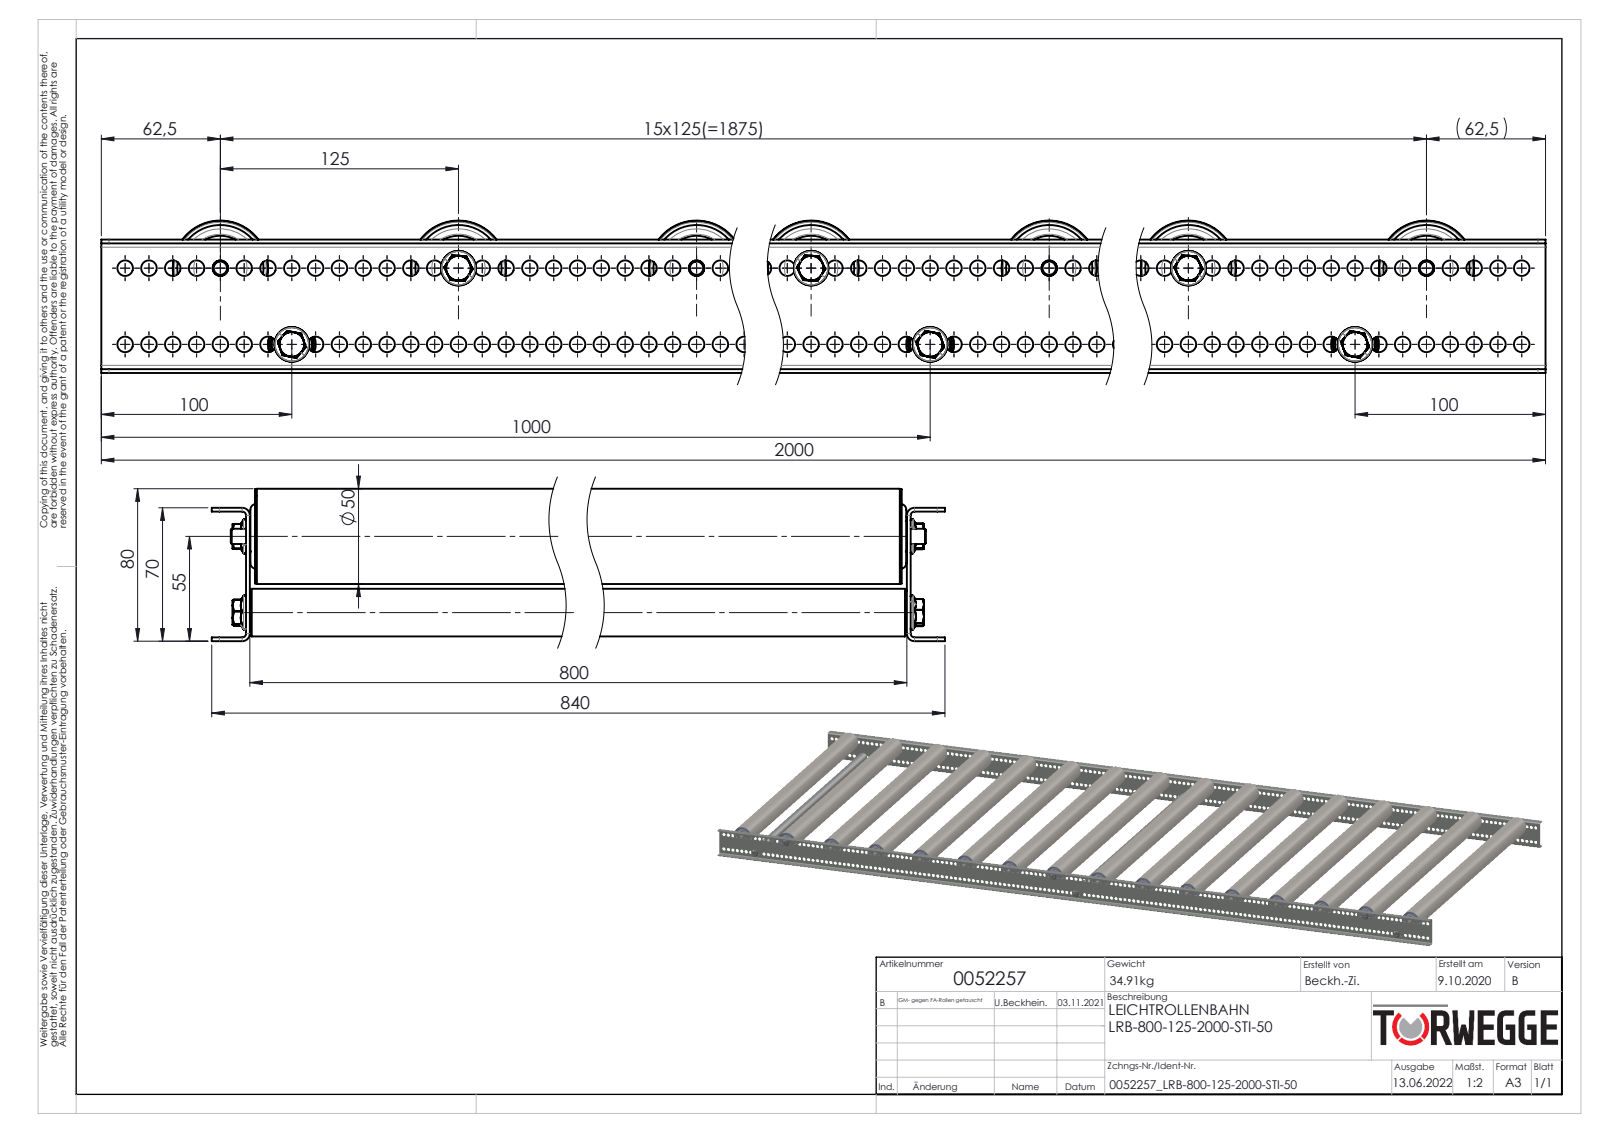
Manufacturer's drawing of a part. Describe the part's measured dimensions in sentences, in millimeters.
The part is named "0026295_Typ-TRG_50x1,5-8; Traversen_KFG_L800; 0026293_Typ-TRG-50x1,5-12; 0052257 (+8 more)". Its 3-D file was written by "SolidWorks 2020 (AUTOMOTIVE_DESIGN)". It is 392 solids with 7558 faces: 1452 planar, 2944 cylindrical and 3162 other. Overall it measures 2000 by 840 by 80 millimeters. Its volume is 5 144 000 cubic millimeters and its surface area 5 873 000 square millimeters. Round holes: 318 of diameter 8.2, 16 of diameter 17.1, 16 of diameter 18.5, 16 of diameter 27.7, 16 of diameter 45.3, 16 of diameter 47, 13 of diameter 7.6, 6 of diameter 6.8, 3 of diameter 12, 3 of diameter 12.2, 3 of diameter 19.2, 3 of diameter 21. Round bosses or shafts: 19 of diameter 8, 16 of diameter 50, 16 of diameter 49.5, 16 of diameter 47.3, 16 of diameter 29.7, 16 of diameter 27.4, 16 of diameter 27.3, 16 of diameter 16. Partial cylindrical surfaces (rounded edges, fillets, slot ends): 26 of radius 0.6, 26 of radius 0.75, 26 of radius 2.45, 13 of radius 4.87, 13 of radius 7, 12 of radius 2.5, 8 of radius 4, 4 of radius 2. The main face-to-face distances are 2, 802, 68, 800, 804, 70, 66, 1, 20, 18. The hole center spacings are 12.5, 25, 37.5, 50, 62.5, 75, 87.5, 100.
